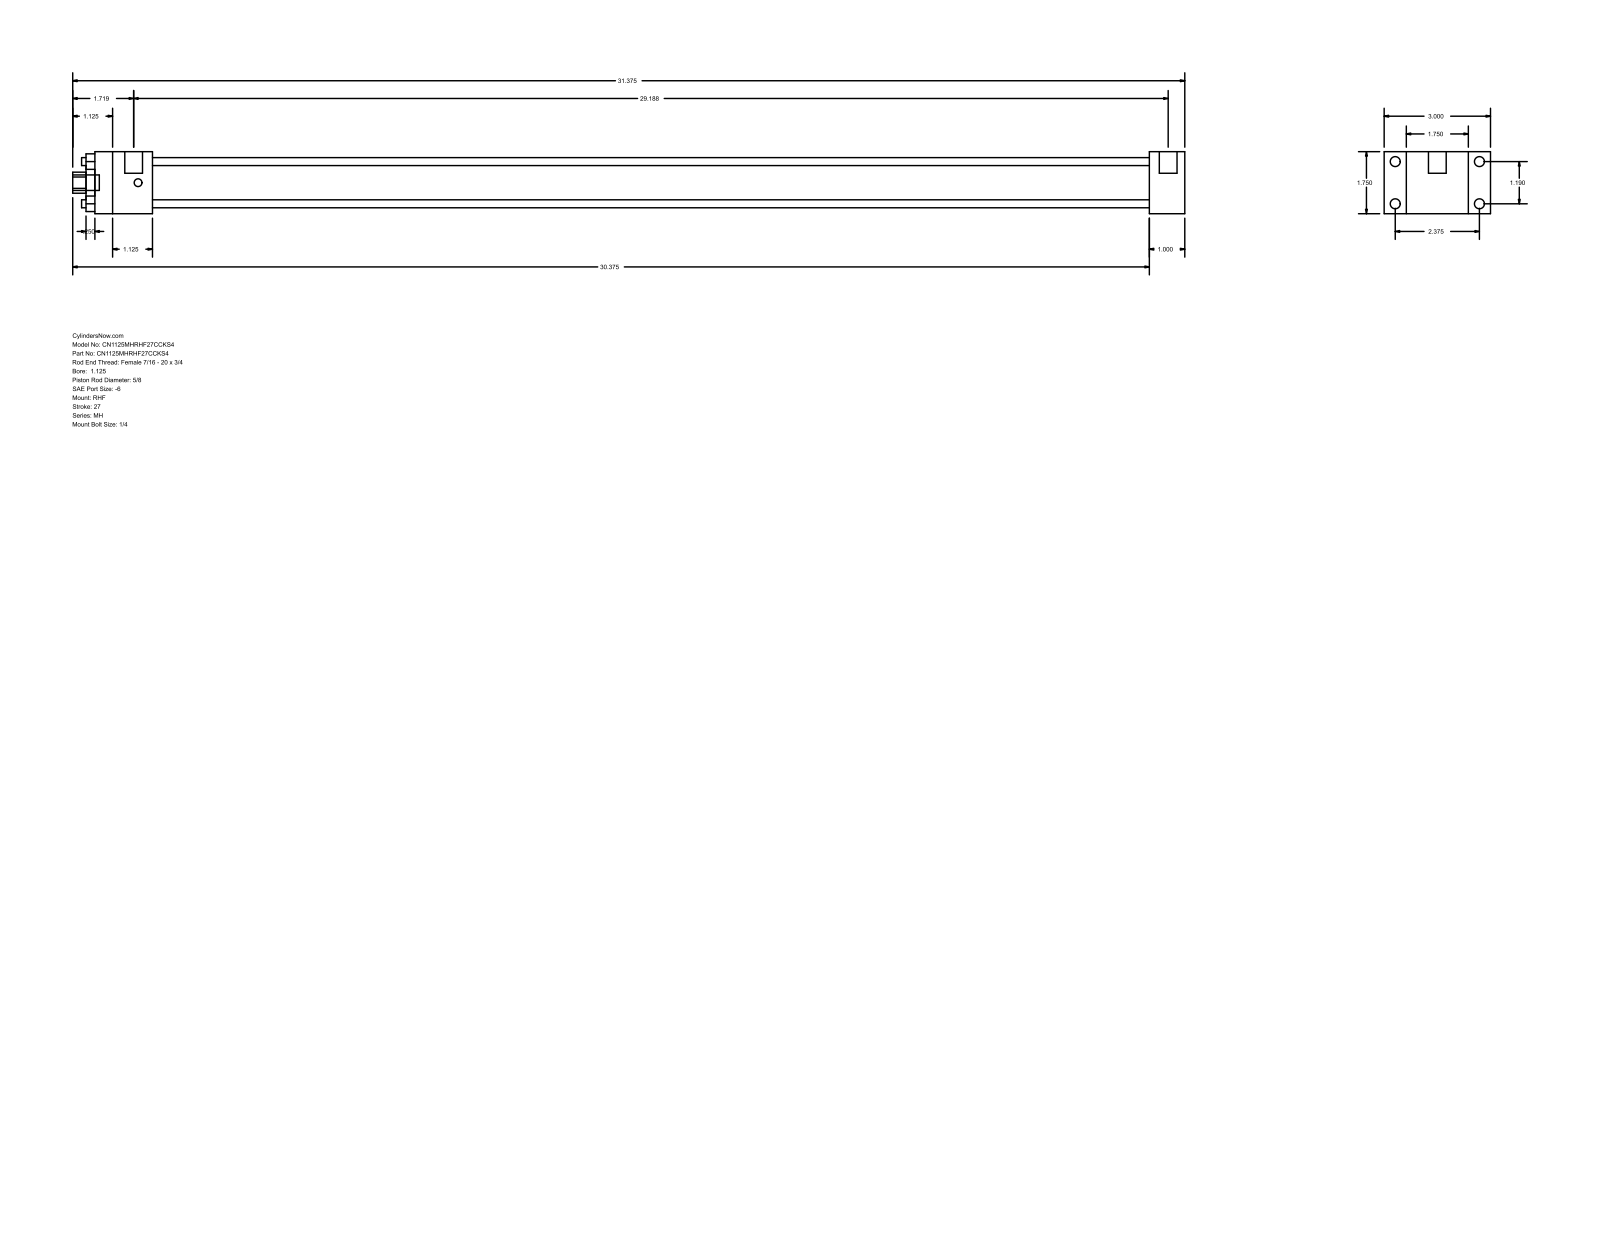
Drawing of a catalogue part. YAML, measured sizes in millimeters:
part_name: "MH_RHF__0112_0.625"
step_written_by: "GSSL Pune (CONFIG_CONTROL_DESIGN)"
units: millimeters
bodies: {solids: 0, faces: 88, planar: 60, cylindrical: 28, other: 0}
overall_size: [796.92, 76.2, 44.45]
round_holes:
  - {diameter: 5.71, count: 4}
  - {diameter: 15.88, count: 1}
  - {diameter: 28.57, count: 1}
  - {diameter: 34.92, count: 1}
round_bosses_or_shafts:
  - {diameter: 7.14, count: 4}
  - {diameter: 5.56, count: 4}
  - {diameter: 12.7, count: 2}
  - {diameter: 11.11, count: 1}
partial_cylinders:
  - {radius: 7.54, count: 1}
face_to_face_distances: [44.46, 15.87, 60.33, 25.4, 76.2, 714.37, 739.77, 41.27, 755.64, 781.04]
hole_center_spacings: [21.37, 30.22, 42.74]
